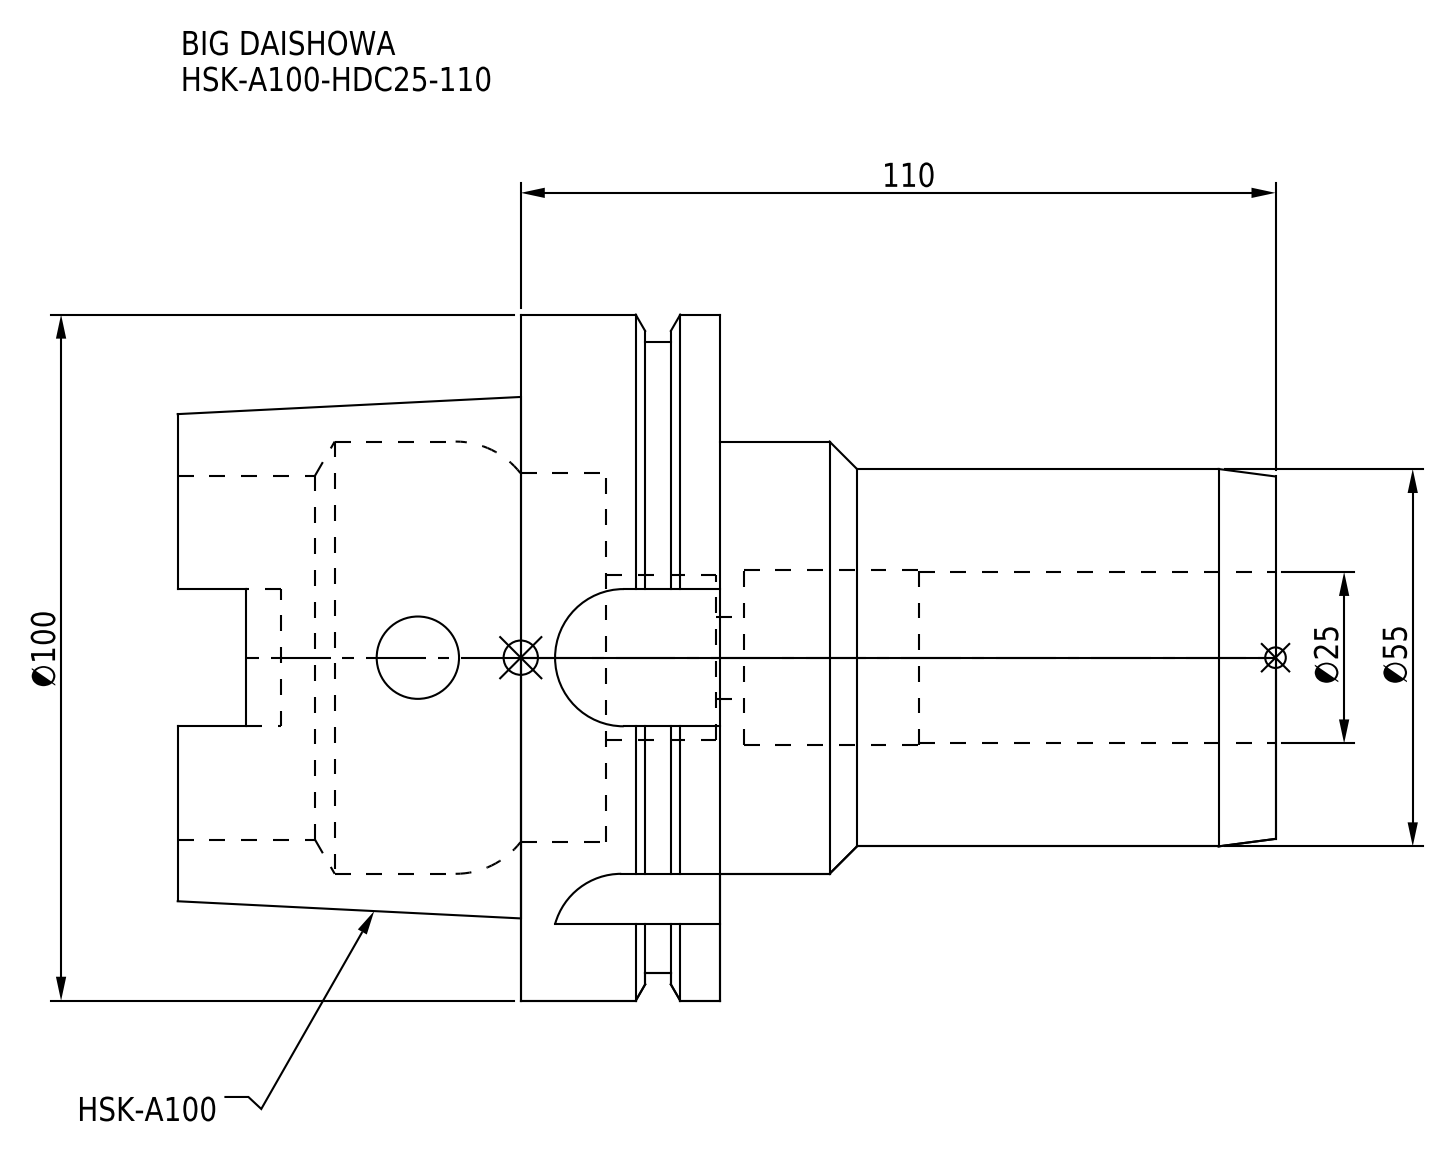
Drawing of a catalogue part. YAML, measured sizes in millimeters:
part_name: "HSK-A100-HDC25-110"
step_written_by: "CREO PARAMETRIC BY PTC INC, 2016380 (AUTOMOTIVE_DESIGN)"
units: millimeters
bodies: {solids: 1, faces: 92, planar: 34, cylindrical: 40, other: 18}
overall_size: [160, 100, 100]
volume: 419471
surface_area: 69900
round_holes:
  - {diameter: 12, count: 2}
  - {diameter: 24, count: 1}
  - {diameter: 25, count: 1}
  - {diameter: 25.5, count: 1}
  - {diameter: 53, count: 1}
  - {diameter: 53.8, count: 1}
  - {diameter: 63, count: 1}
round_bosses_or_shafts:
  - {diameter: 100, count: 1}
  - {diameter: 92, count: 1}
  - {diameter: 55, count: 1}
partial_cylinders:
  - {radius: 4.88, count: 4}
  - {radius: 10, count: 4}
face_to_face_distances: [29, 16.55, 12.45, 81, 97.55, 110, 160, 79, 62.45, 50]
